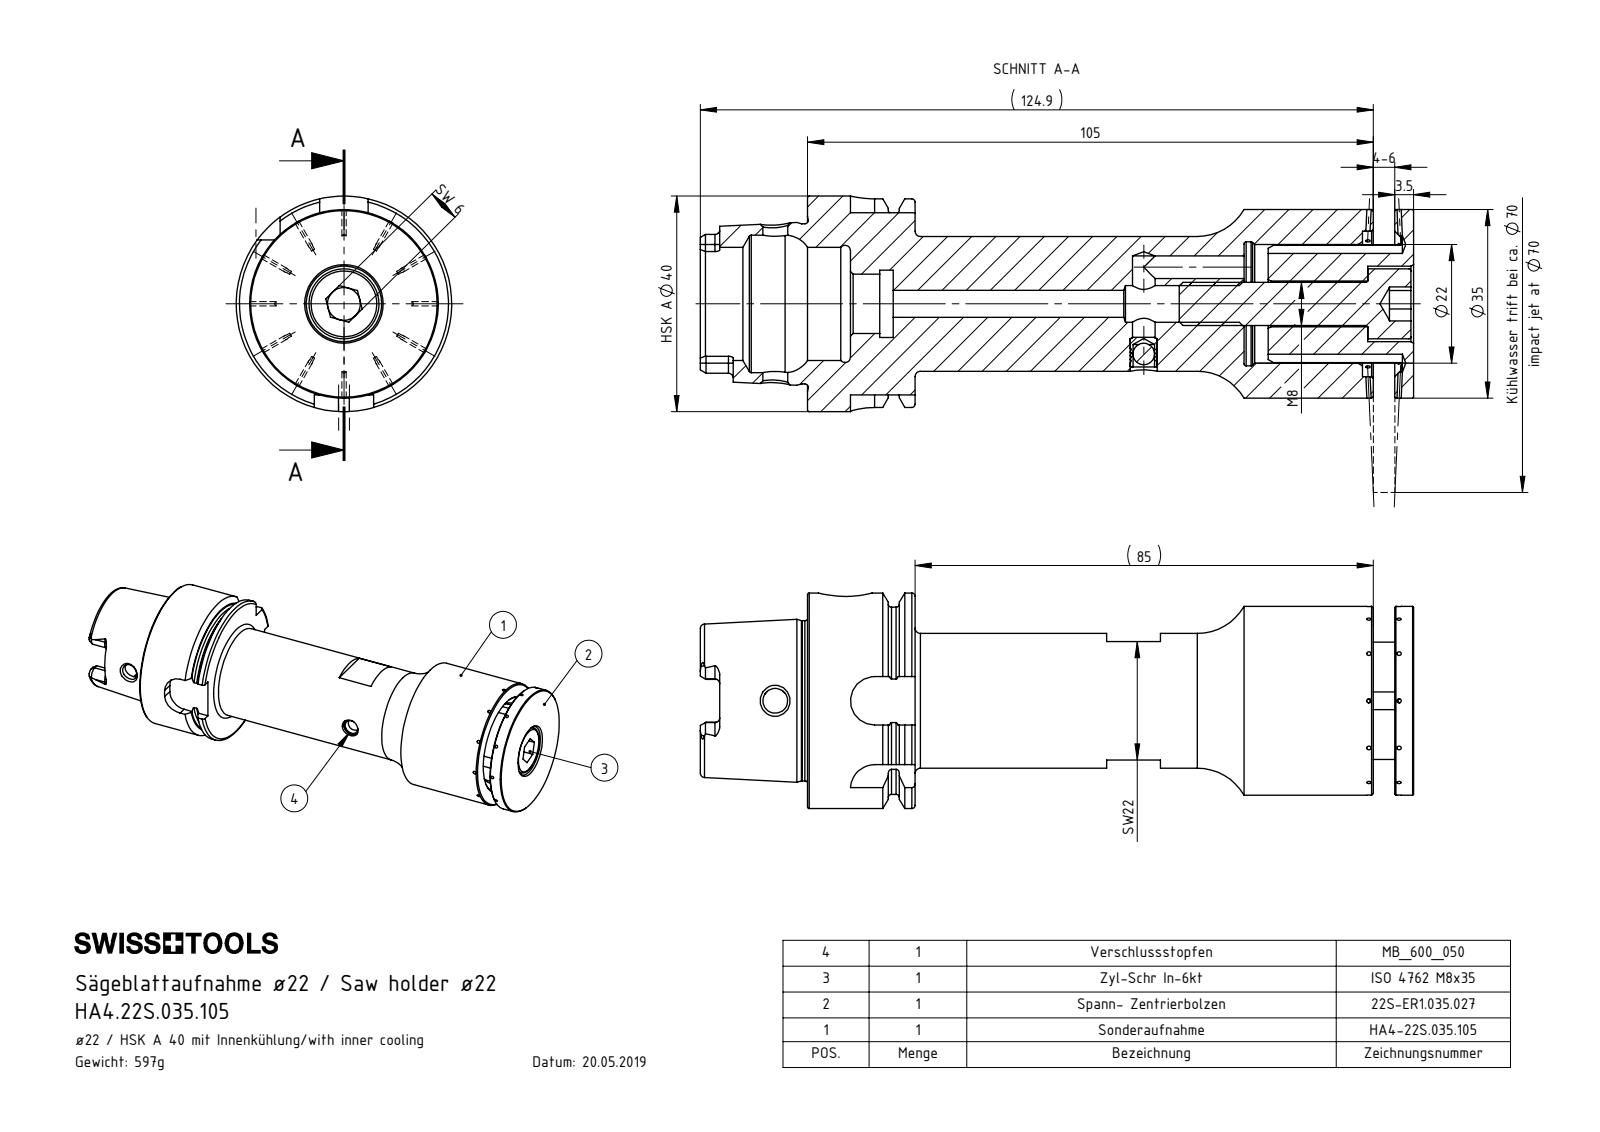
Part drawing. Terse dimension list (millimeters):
name: HA4-22S.035.105_A_Fertigbearbeitung; HA4.22S.035.105; KVT_MB_600_050; ISO 4762 - M8 x 35 (+1 more)
written by: SolidWorks 2017 (AUTOMOTIVE_DESIGN)
unit: mm
bodies: 5 solids, 264 faces (77 planar, 81 cylindrical, 106 other)
size: 132.4 × 40 × 40
volume: 78 349 mm³; area: 27 778 mm²
holes: 24× ⌀0.8, 4× ⌀3.3, 2× ⌀4.2, 1× ⌀4, 1× ⌀4.6, 1× ⌀5, 1× ⌀6.8, 1× ⌀8.5, 1× ⌀10, 1× ⌀11, 1× ⌀12.5, 1× ⌀14
bosses: 1× ⌀40, 1× ⌀35, 1× ⌀34.75, 1× ⌀29.71, 1× ⌀25, 1× ⌀22, 1× ⌀13, 1× ⌀8
rounds: 6× R0.9, 4× R1.88, 4× R4.5
face distances: 92.55, 19.95, 112.5, 109, 89.05, 3.5, 61.05, 1, 105, 85.05
hole spacings: 7.15, 11, 15.56, 12.93, 22, 4.2, 6.8, 17.8
